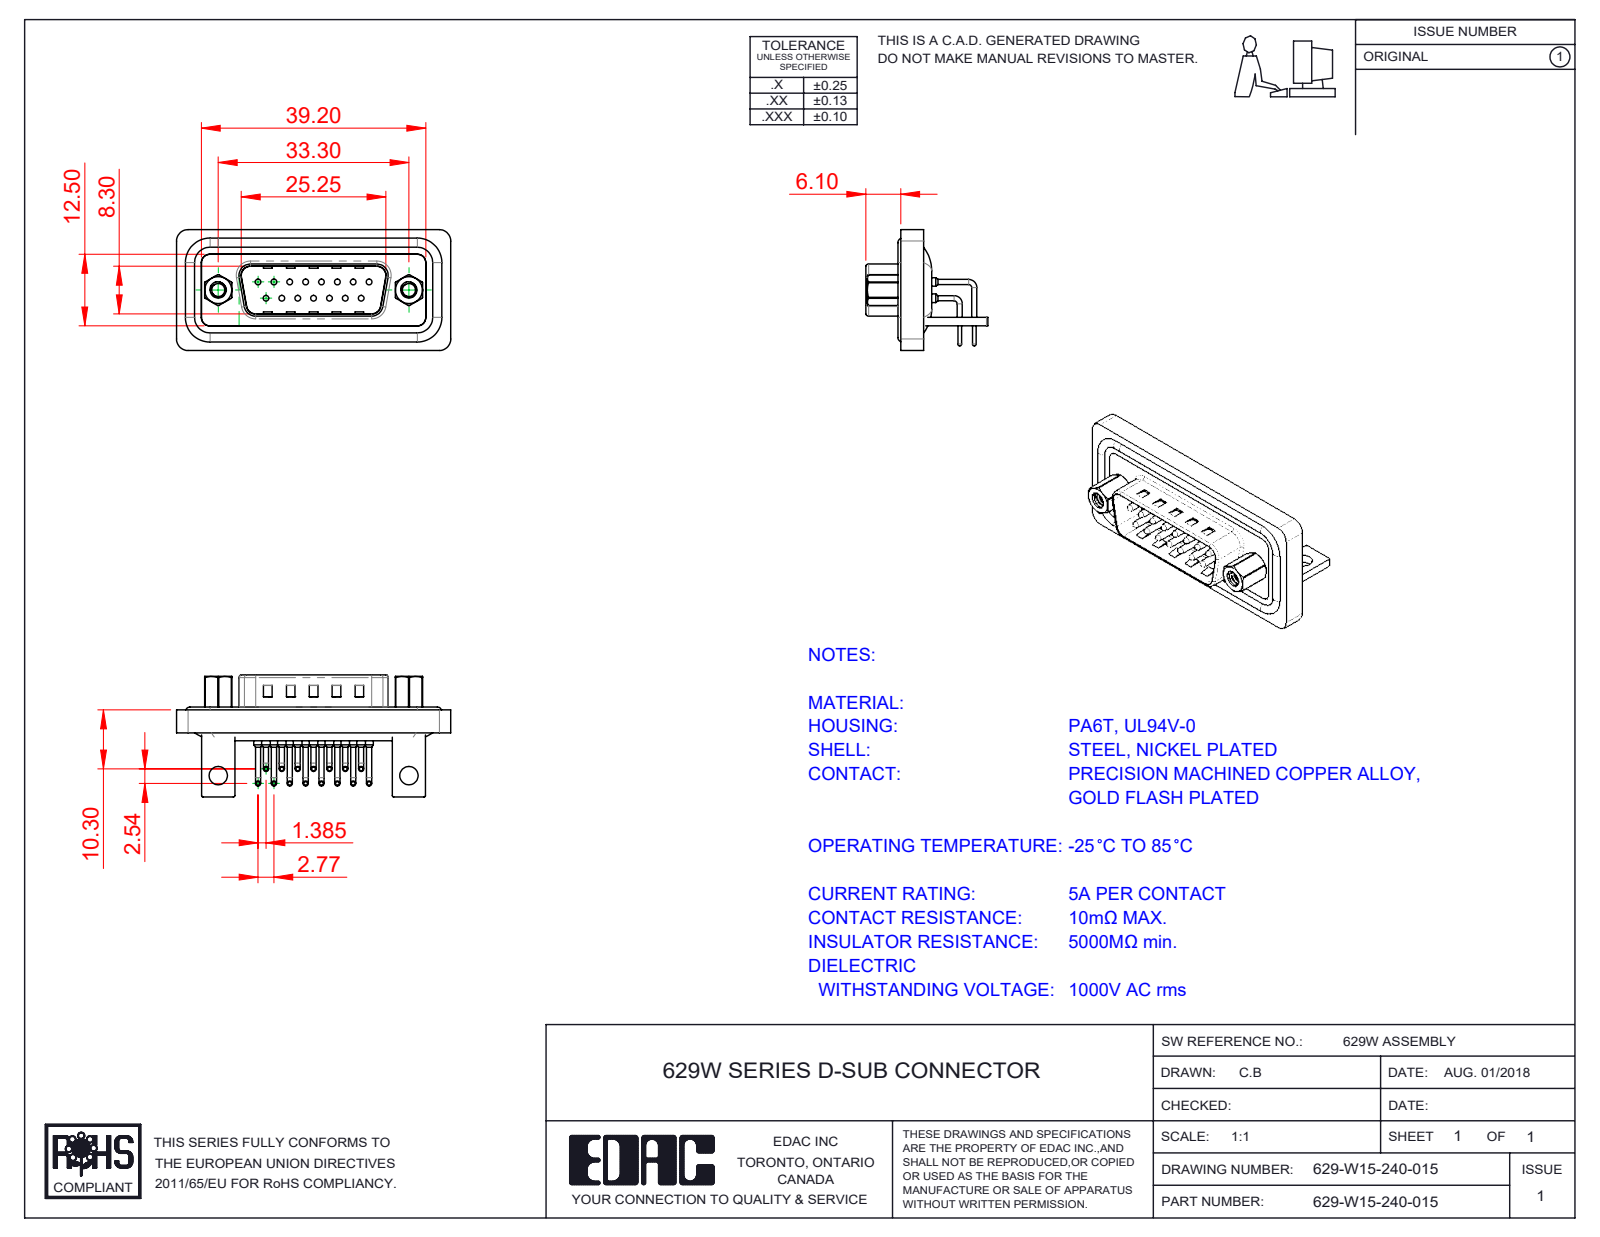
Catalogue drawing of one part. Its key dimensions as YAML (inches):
part_name: "629-W15-240-015; 629W Stabilizer Bracket; 629W 4-40 Hex Standoff; 629W Contact Row 2 (+5 more)"
step_written_by: "SolidWorks 2016 (CONFIG_CONTROL_DESIGN)"
units: inches
bodies: {solids: 25, faces: 2210, planar: 1155, cylindrical: 806, other: 249}
overall_size: [1.885, 0.839, 0.831]
volume: 0.32
surface_area: 14.17
round_holes:
  - {diameter: 0.039, count: 15}
  - {diameter: 0.059, count: 15}
  - {diameter: 0.067, count: 15}
  - {diameter: 0.079, count: 15}
  - {diameter: 0.089, count: 2}
  - {diameter: 0.09, count: 2}
  - {diameter: 0.126, count: 2}
  - {diameter: 0.157, count: 2}
  - {diameter: 0.189, count: 2}
  - {diameter: 0.193, count: 2}
  - {diameter: 0.197, count: 2}
round_bosses_or_shafts:
  - {diameter: 0.035, count: 30}
  - {diameter: 0.059, count: 15}
  - {diameter: 0.026, count: 15}
  - {diameter: 0.063, count: 4}
  - {diameter: 0.11, count: 2}
  - {diameter: 0.197, count: 1}
partial_cylinders:
  - {radius: 0.079, count: 17}
  - {radius: 0.04, count: 15}
  - {radius: 0.059, count: 14}
  - {radius: 0.01, count: 12}
  - {radius: 0.02, count: 9}
  - {radius: 0.106, count: 6}
  - {radius: 0.035, count: 4}
  - {radius: 0.063, count: 4}
face_to_face_distances: [0.016, 0.063, 0.043, 0.098, 0.114, 0.169, 0.059, 0.02, 0.083, 0.161]
hole_center_spacings: [0.124, 0.109, 0.218, 0.327, 0.125, 0.124, 0.436, 0.198]
